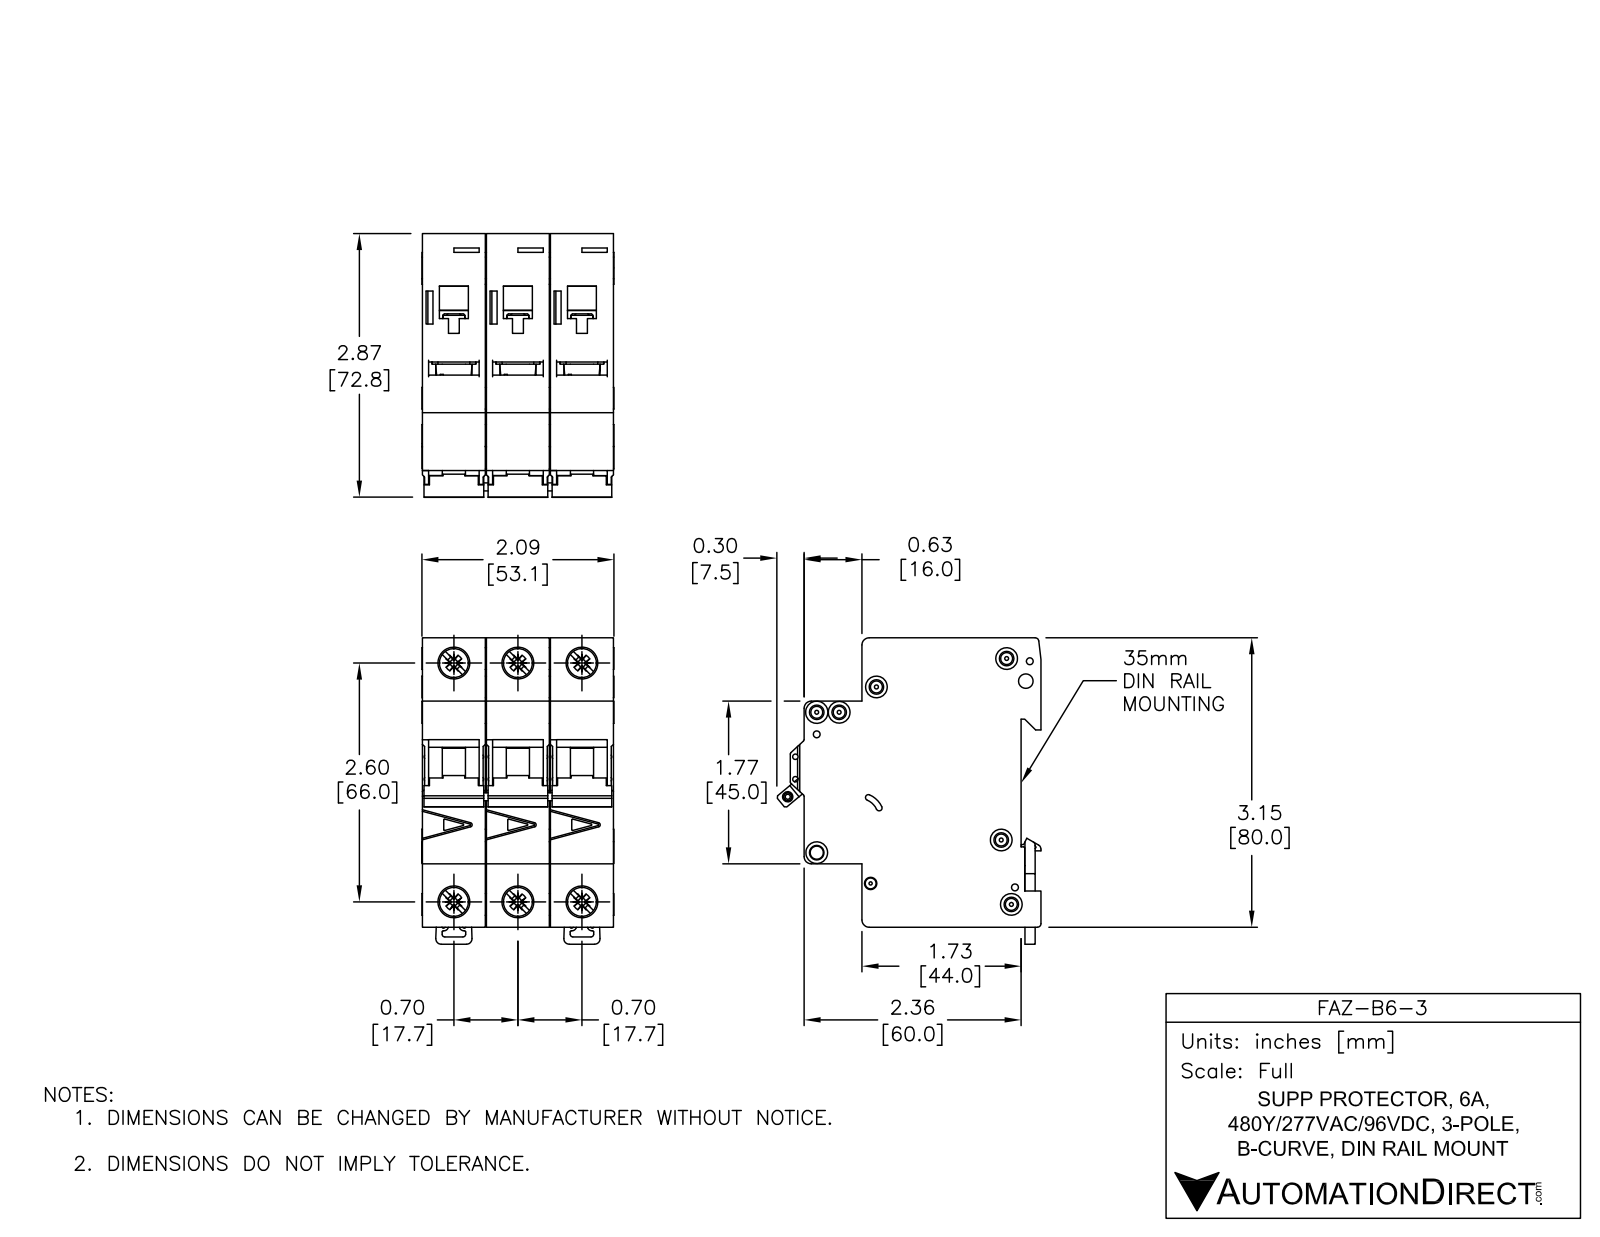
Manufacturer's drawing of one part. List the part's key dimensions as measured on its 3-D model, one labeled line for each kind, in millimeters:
Part name (STEP PRODUCT): FAZ-B6-3
STEP written by: SolidWorks 2014 (AUTOMOTIVE_DESIGN)
Units: millimetres
Bodies: 11 solids, 1650 faces (697 planar, 590 cylindrical, 363 other)
Overall size (bounding box): 84.78 × 73.04 × 53.1
Volume: 224 680 mm³ · Surface area: 58 052 mm²
Round holes (diameter × count): ⌀3.6 ×6, ⌀8.2 ×4, ⌀1.9 ×3, ⌀1.09 ×2, ⌀1.5 ×2, ⌀4 ×2, ⌀7.15 ×2, ⌀2.15 ×1, ⌀2.2 ×1, ⌀2.55 ×1, ⌀3.3 ×1, ⌀3.4 ×1
Round bosses / shafts (diameter × count): ⌀6 ×4, ⌀2.5 ×3, ⌀8.2 ×2
Partial cylindrical surfaces — rounded edges, fillets, slot ends (radius × count): R0.25 ×68, R0.5 ×25, R1 ×12, R2 ×12, R0.2 ×11, R1.8 ×3, R0.8 ×2, R3 ×2
Main face-to-face distances: 17.7, 17.5, 35.4, 35.2, 52.9, 17.9, 79.48, 5.5, 49.5, 44
Hole centre spacings: 17.7, 68.33, 66, 6.2, 13.64, 35.4, 74.89, 4.81
